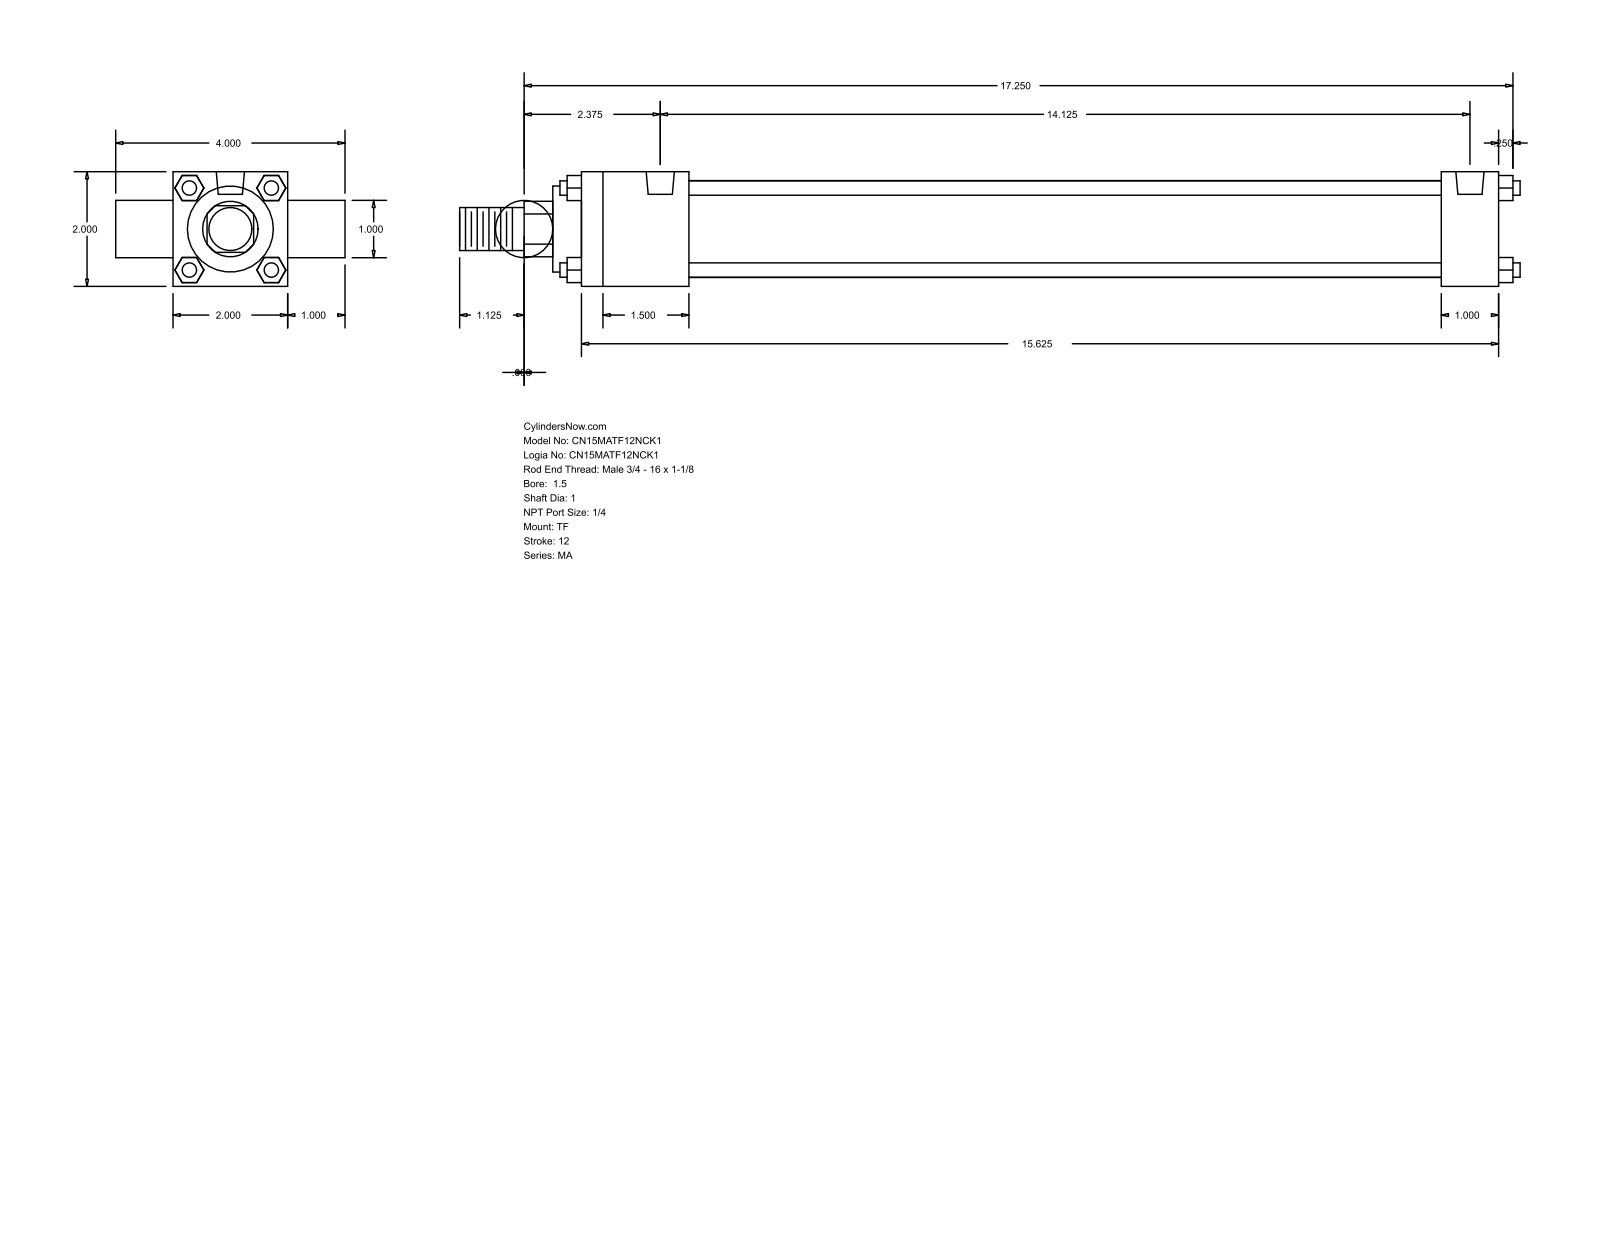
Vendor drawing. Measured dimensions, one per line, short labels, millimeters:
name: MA_TF__0150_1
written by: GSSL Pune (CONFIG_CONTROL_DESIGN)
unit: mm
bodies: 0 solids, 120 faces (92 planar, 28 cylindrical, 0 other)
size: 469.9 × 101.6 × 50.8
holes: 3× ⌀7.94, 2× ⌀12.49
bosses: 4× ⌀6.35, 2× ⌀25.4, 1× ⌀42.93, 1× ⌀38.1, 1× ⌀19.05
rounds: 1× R12.29
face distances: 50.8, 25.4, 406.4, 76.2, 6.35, 47.63, 381, 333.37, 358.77, 419.1
hole spacings: 358.77
